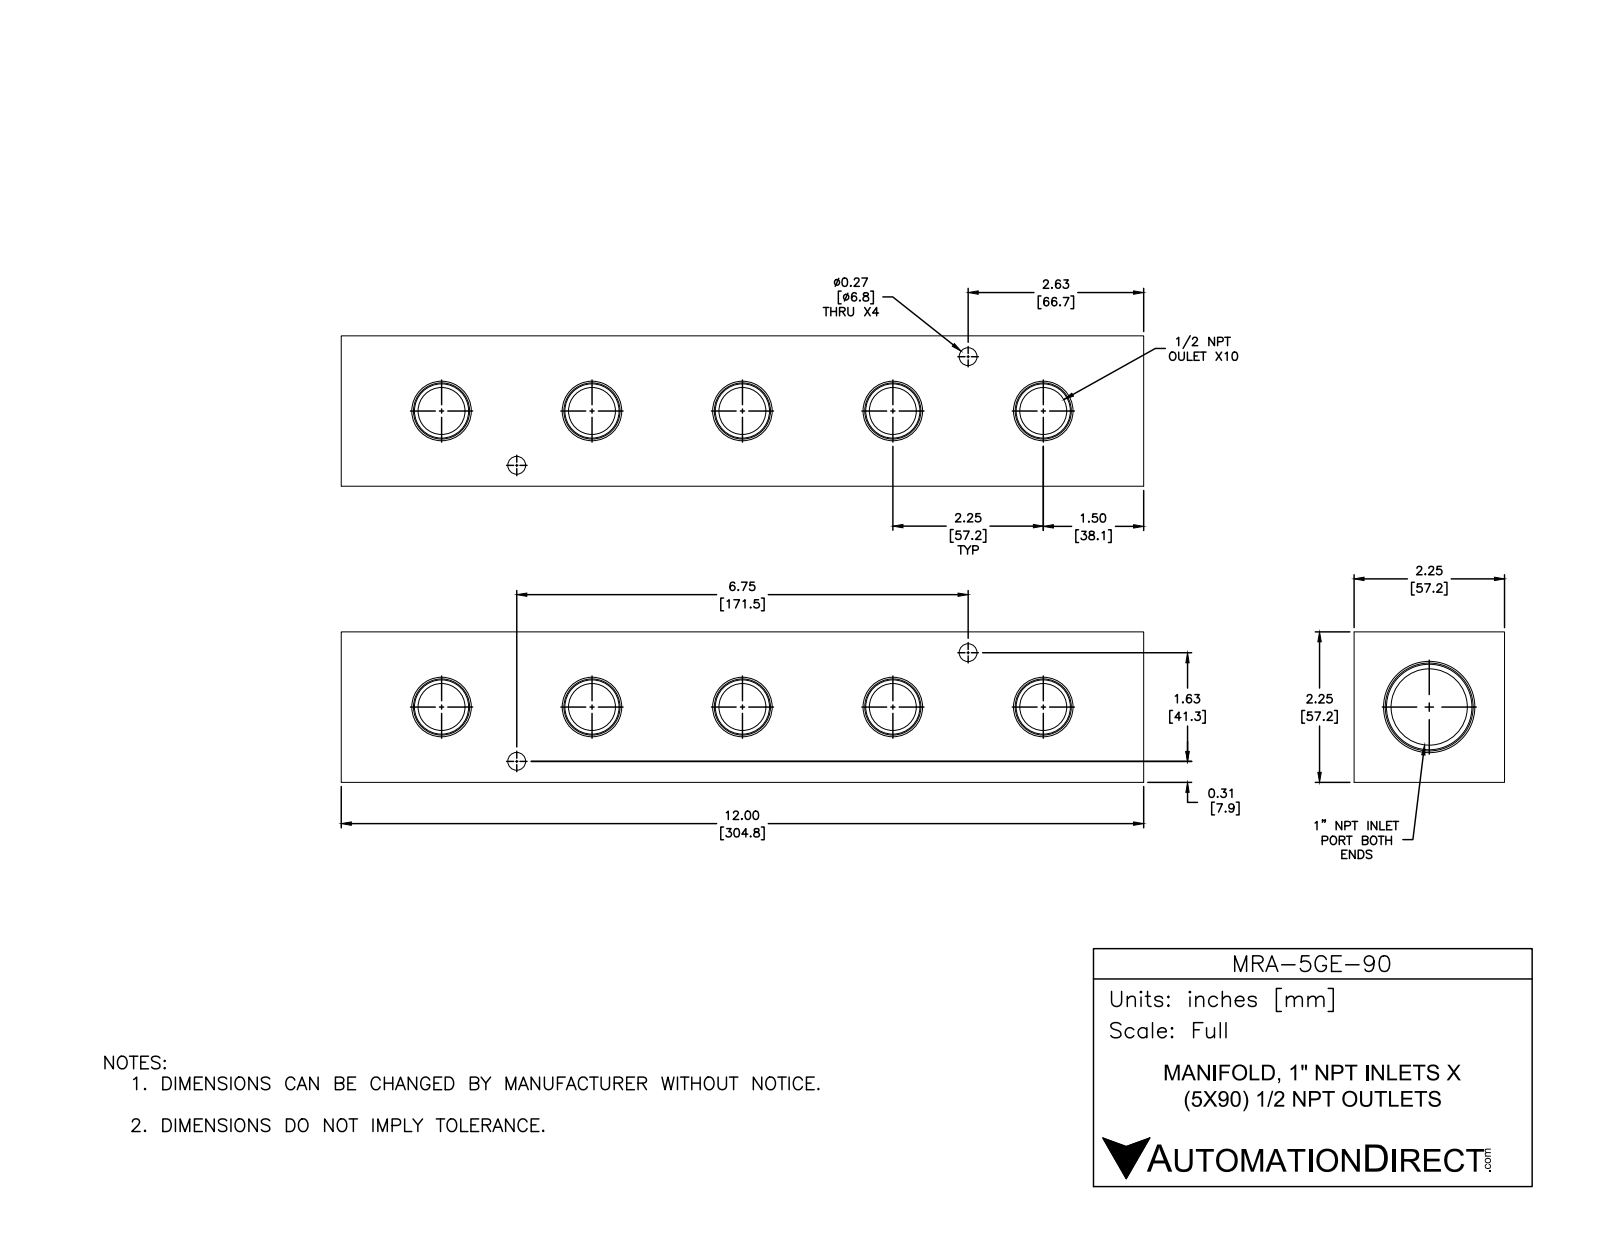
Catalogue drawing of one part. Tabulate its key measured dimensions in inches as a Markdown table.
| quantity | value |
| --- | --- |
| part name | MRA-5GE-90 |
| STEP written by | SolidWorks 2015 (CONFIG_CONTROL_DESIGN) |
| units | inches |
| bodies | 1 solid, 104 faces (18 planar, 38 cylindrical, 48 other) |
| overall size | 12 × 2.25 × 2.25 |
| volume | 44.56 in³ |
| surface area | 172.8 in² |
| round holes (diameter × count) | 0.703 × 10, 0.266 × 4, 1.141 × 1 |
| main face-to-face distances | 2.25, 12, 0.53, 1.72, 0.66, 11.34, 10.68 |
| hole center spacings | 1.388, 2.25, 4.5, 6.75, 3.471, 3.472, 5.683, 5.683 |
